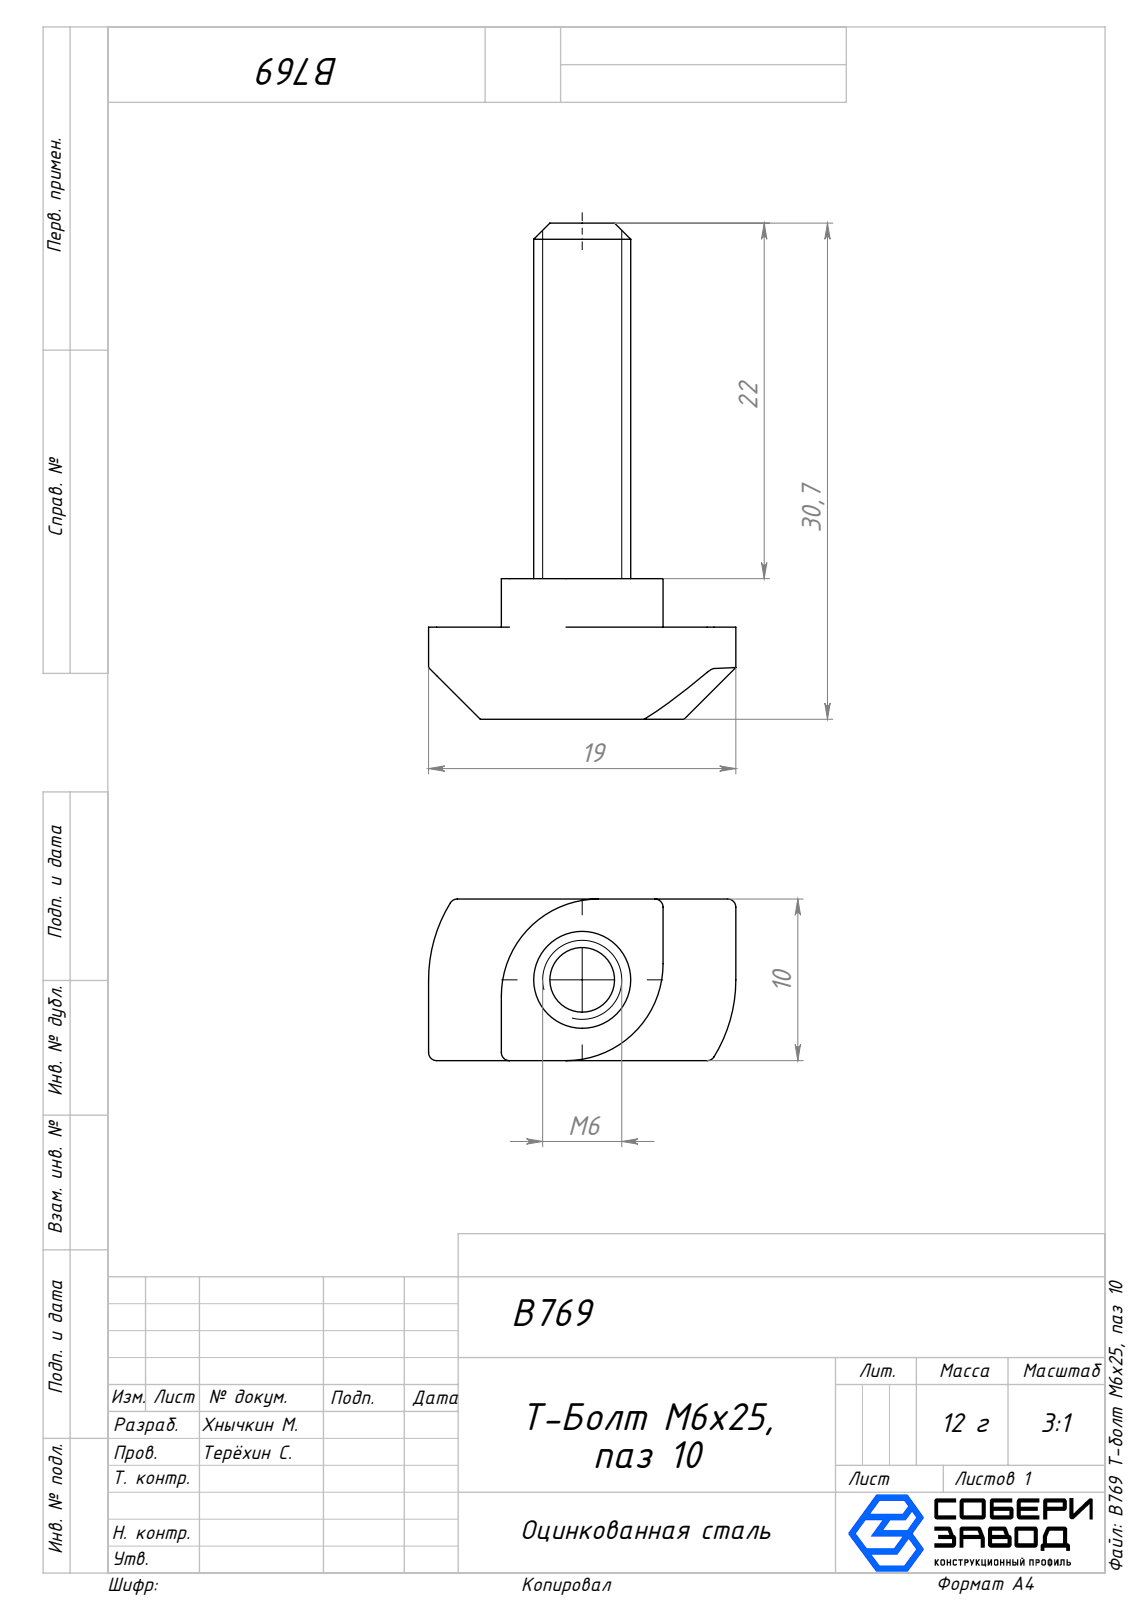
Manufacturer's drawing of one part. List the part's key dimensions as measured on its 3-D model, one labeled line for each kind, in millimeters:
Part name (STEP PRODUCT): B769 Т-болт М6х25, паз 10
STEP written by: SolidWorks 2025 (AUTOMOTIVE_DESIGN)
Units: millimetres
Bodies: 1 solid, 29 faces (13 planar, 12 cylindrical, 4 other)
Overall size (bounding box): 30.7 × 19 × 10
Volume: 1 817 mm³ · Surface area: 1 131 mm²
Round bosses / shafts (diameter × count): ⌀6 ×1
Partial cylindrical surfaces — rounded edges, fillets, slot ends (radius × count): R0.5 ×6, R6 ×2, R9.08 ×2
Main face-to-face distances: 10, 5.7, 8.7, 3, 4.5, 14.5, 30.7, 25, 22, 19
